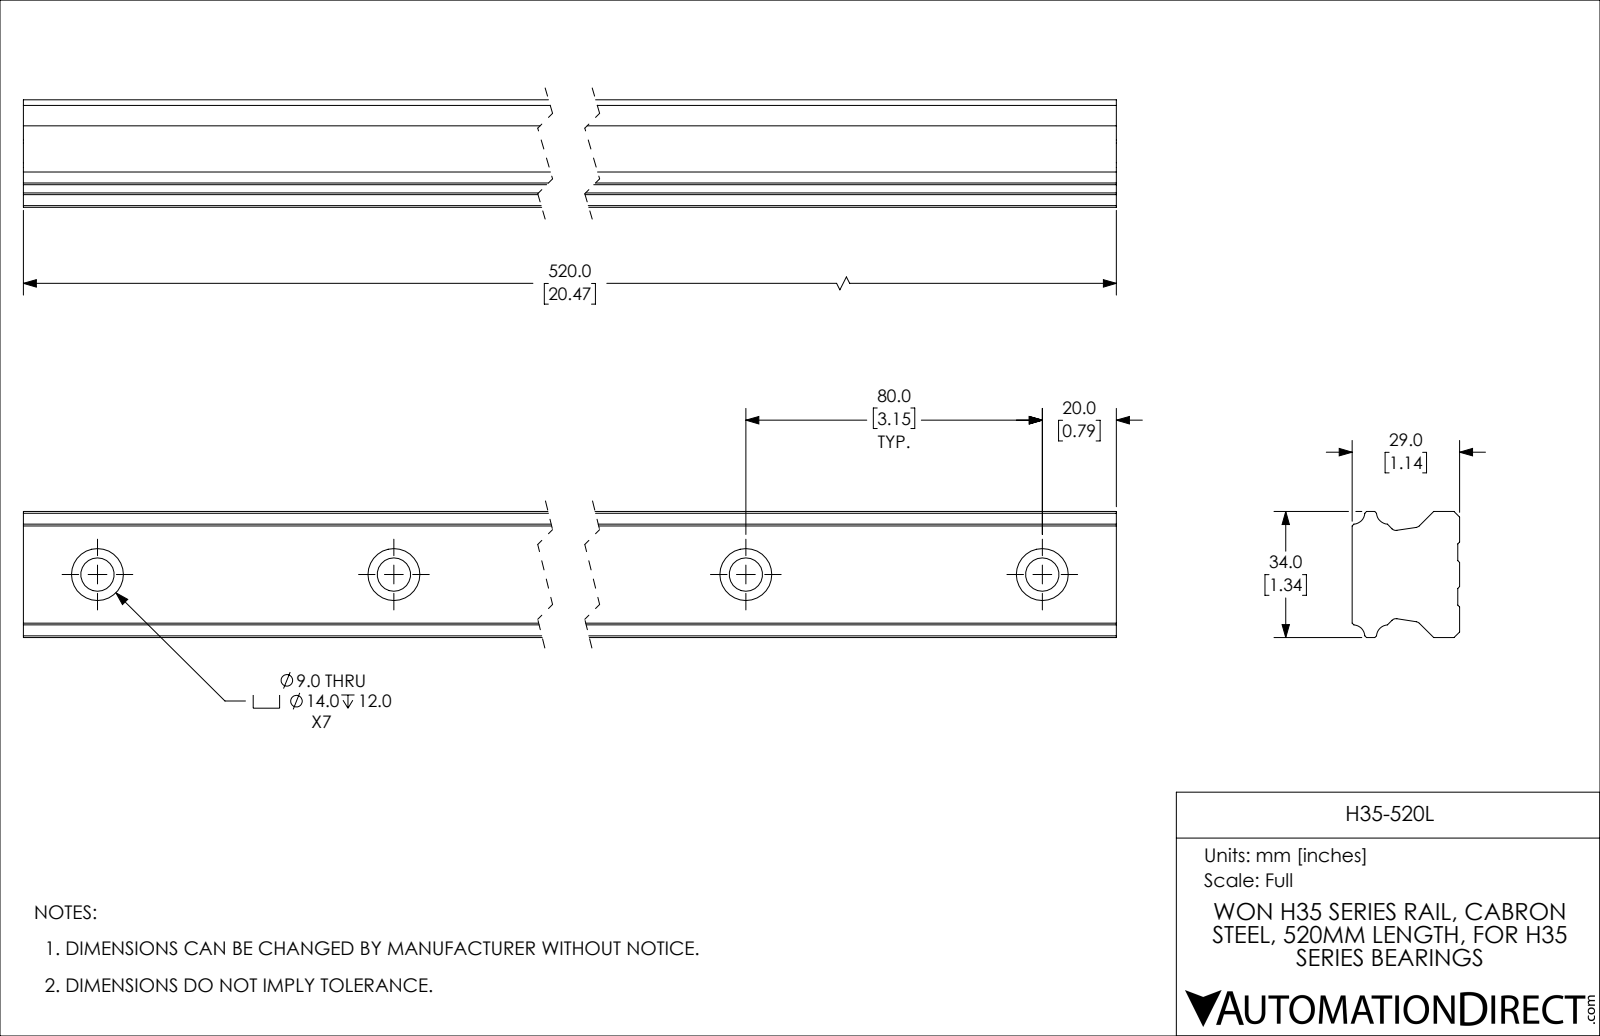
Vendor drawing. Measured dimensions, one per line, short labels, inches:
name: H35-520L
written by: SolidWorks 2019 (CONFIG_CONTROL_DESIGN)
unit: in
bodies: 1 solid, 94 faces (58 planar, 36 cylindrical, 0 other)
size: 20.472 × 1.339 × 1.142
volume: 25.7 in³; area: 116.6 in²
holes: 7× ⌀0.354, 7× ⌀0.551
rounds: 4× R0.059, 4× R0.126
face distances: 1.142, 0.02, 1.122, 1.339, 0.504, 0.596, 1.1, 1.603, 1.007, 0.504
hole spacings: 3.15, 6.299, 9.449, 12.598, 15.748, 18.898
